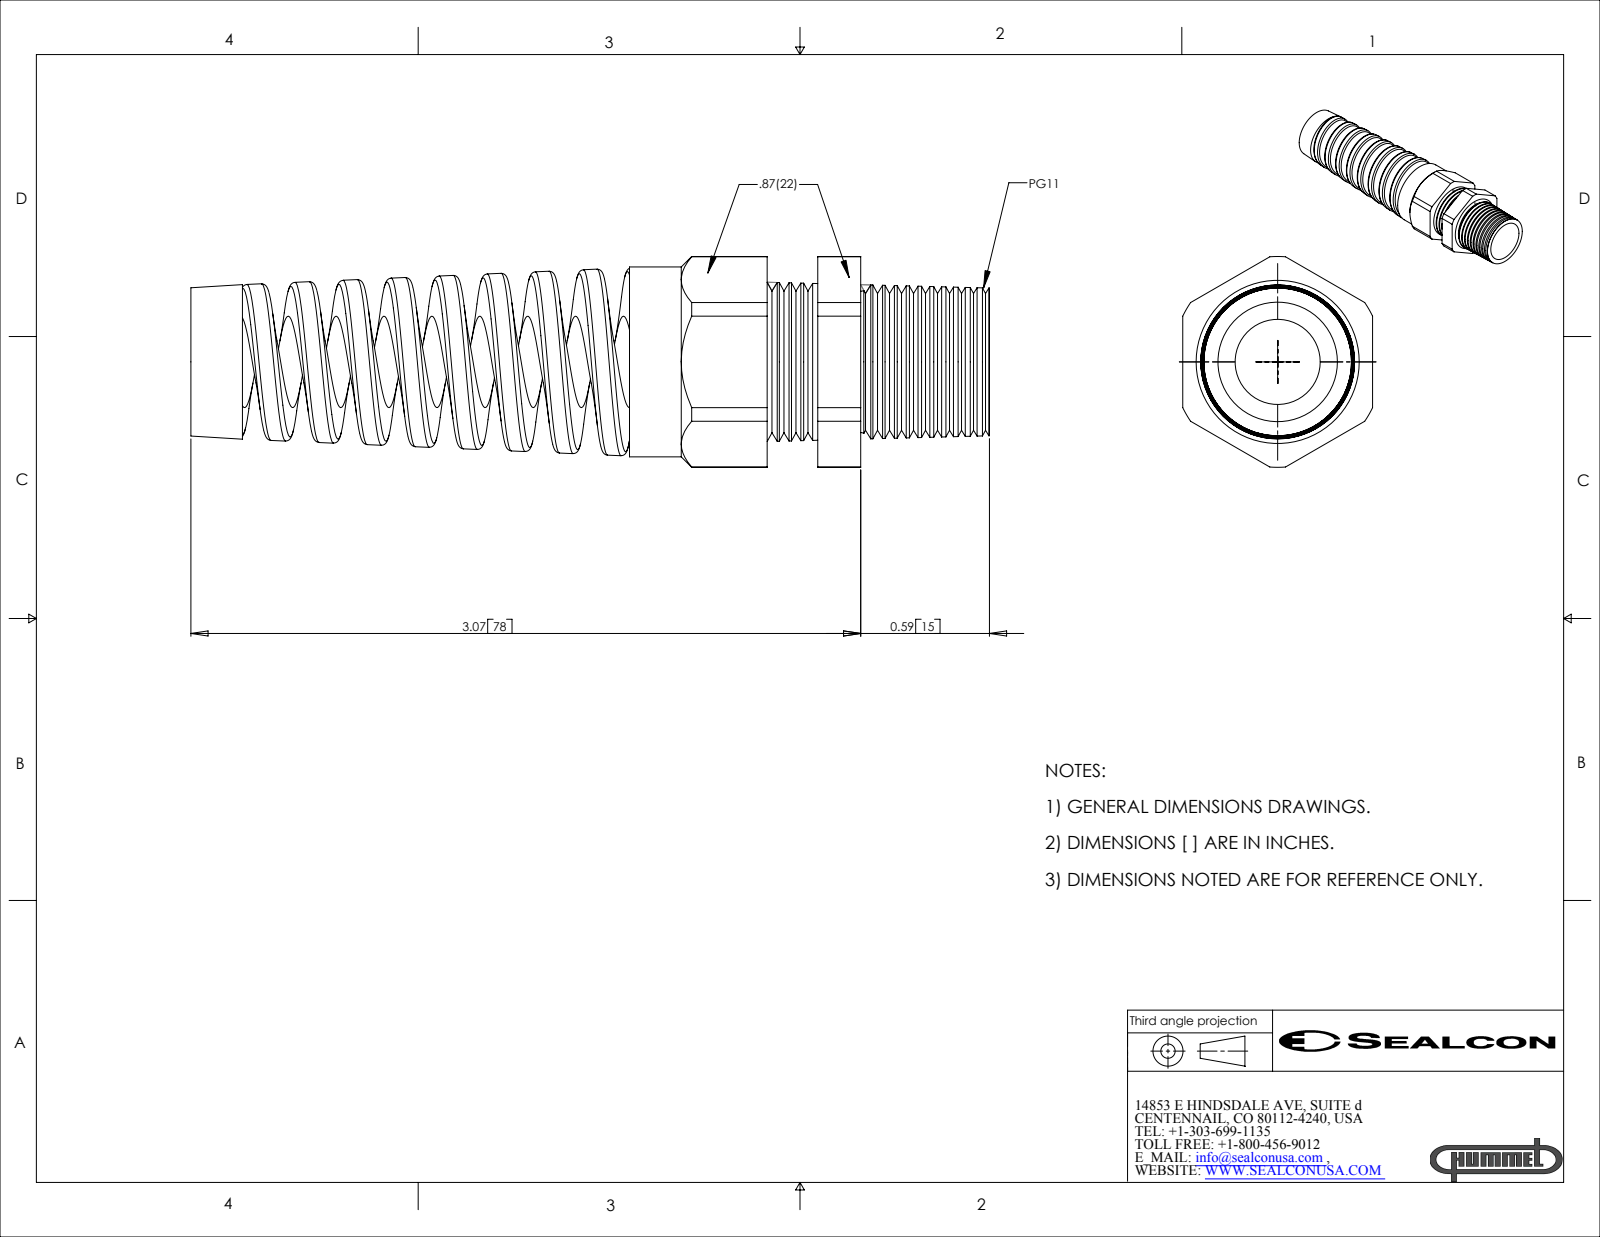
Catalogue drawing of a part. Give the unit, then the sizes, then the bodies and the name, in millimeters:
Units: millimetres
Overall size (bounding box): 93 × 24.5 × 22.1
Round holes (diameter × count): ⌀9.9 ×1, ⌀10.6 ×1, ⌀11.4 ×1
Round bosses / shafts (diameter × count): ⌀22.1 ×1, ⌀13.9 ×1
Partial cylindrical surfaces — rounded edges, fillets, slot ends (radius × count): R12.3 ×1
Main face-to-face distances: 22.1, 5.9, 16, 21.9, 26.9, 10.9, 5, 51.1, 67.1, 73
Volume: 15 500 mm³ · Surface area: 12 610 mm²
Bodies: 2 solids, 196 faces (24 planar, 42 cylindrical, 130 other)
Part name (STEP PRODUCT): CF11CA-GY
STEP written by: SolidWorks 2007 (CONFIG_CONTROL_DESIGN)
